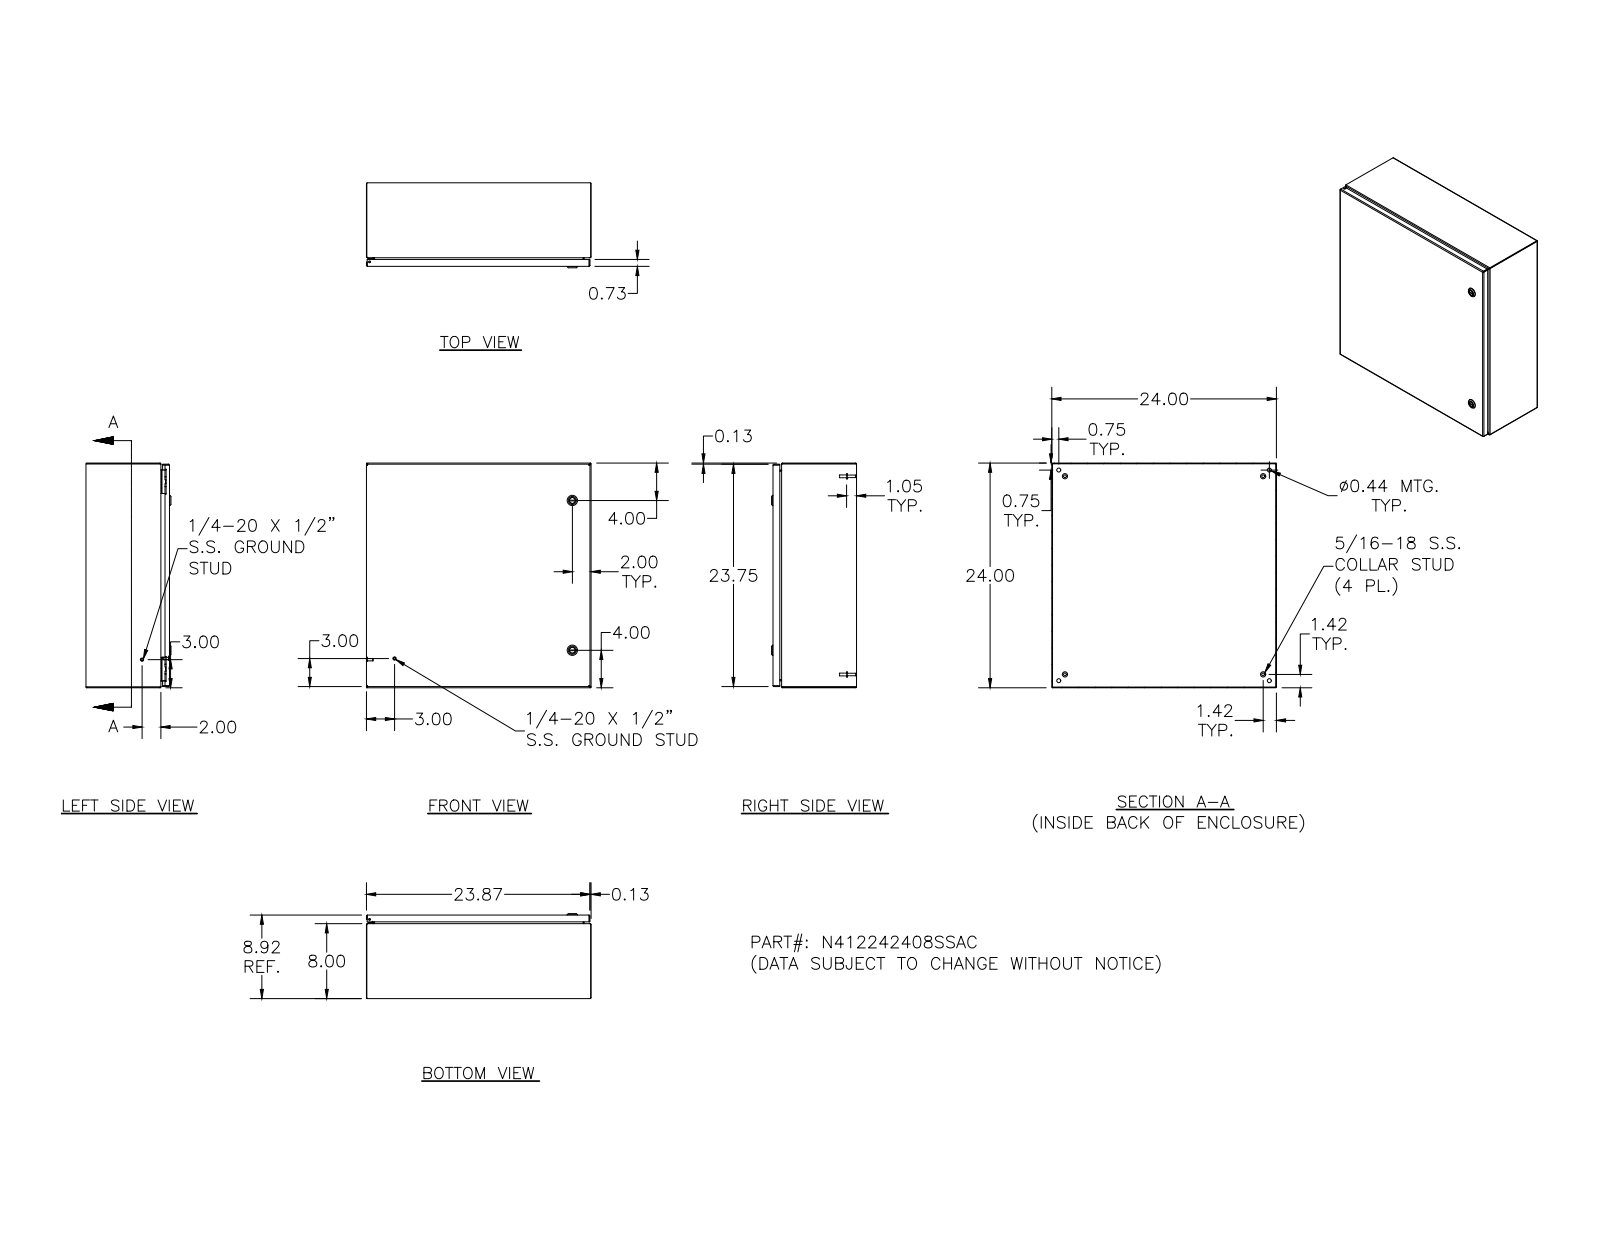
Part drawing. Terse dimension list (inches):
name: N412242408SSAC; N412242408SSACBKP; 388151; N4122424SSACLID (+8 more)
written by: Autodesk Inventor 2011 (AUTOMOTIVE_DESIGN)
unit: in
bodies: 42 solids, 1662 faces (698 planar, 588 cylindrical, 376 other)
size: 24 × 24 × 9.075
volume: 157.1 in³; area: 4 263 in²
holes: 5× ⌀0.188, 4× ⌀0.093, 4× ⌀0.152, 4× ⌀0.167, 4× ⌀0.172, 4× ⌀0.437, 2× ⌀0.156, 2× ⌀0.197, 2× ⌀0.315, 2× ⌀0.394, 2× ⌀0.402, 2× ⌀0.634
bosses: 10× ⌀0.25, 4× ⌀0.563, 4× ⌀0.36, 4× ⌀0.32, 4× ⌀0.3, 4× ⌀0.275, 4× ⌀0.256, 4× ⌀0.164
rounds: 26× R0.05, 18× R0.016, 16× R0.016, 16× R0.09, 15× R0.02, 14× R0.031, 14× R0.125, 8× R0.032
face distances: 0.074, 8.843, 23.926, 8.917, 8.769, 24, 23.852, 7.926, 0.917, 0.739
hole spacings: 20, 0.017, 0.66, 22.5, 22.869, 0.019, 0.5, 0.648
